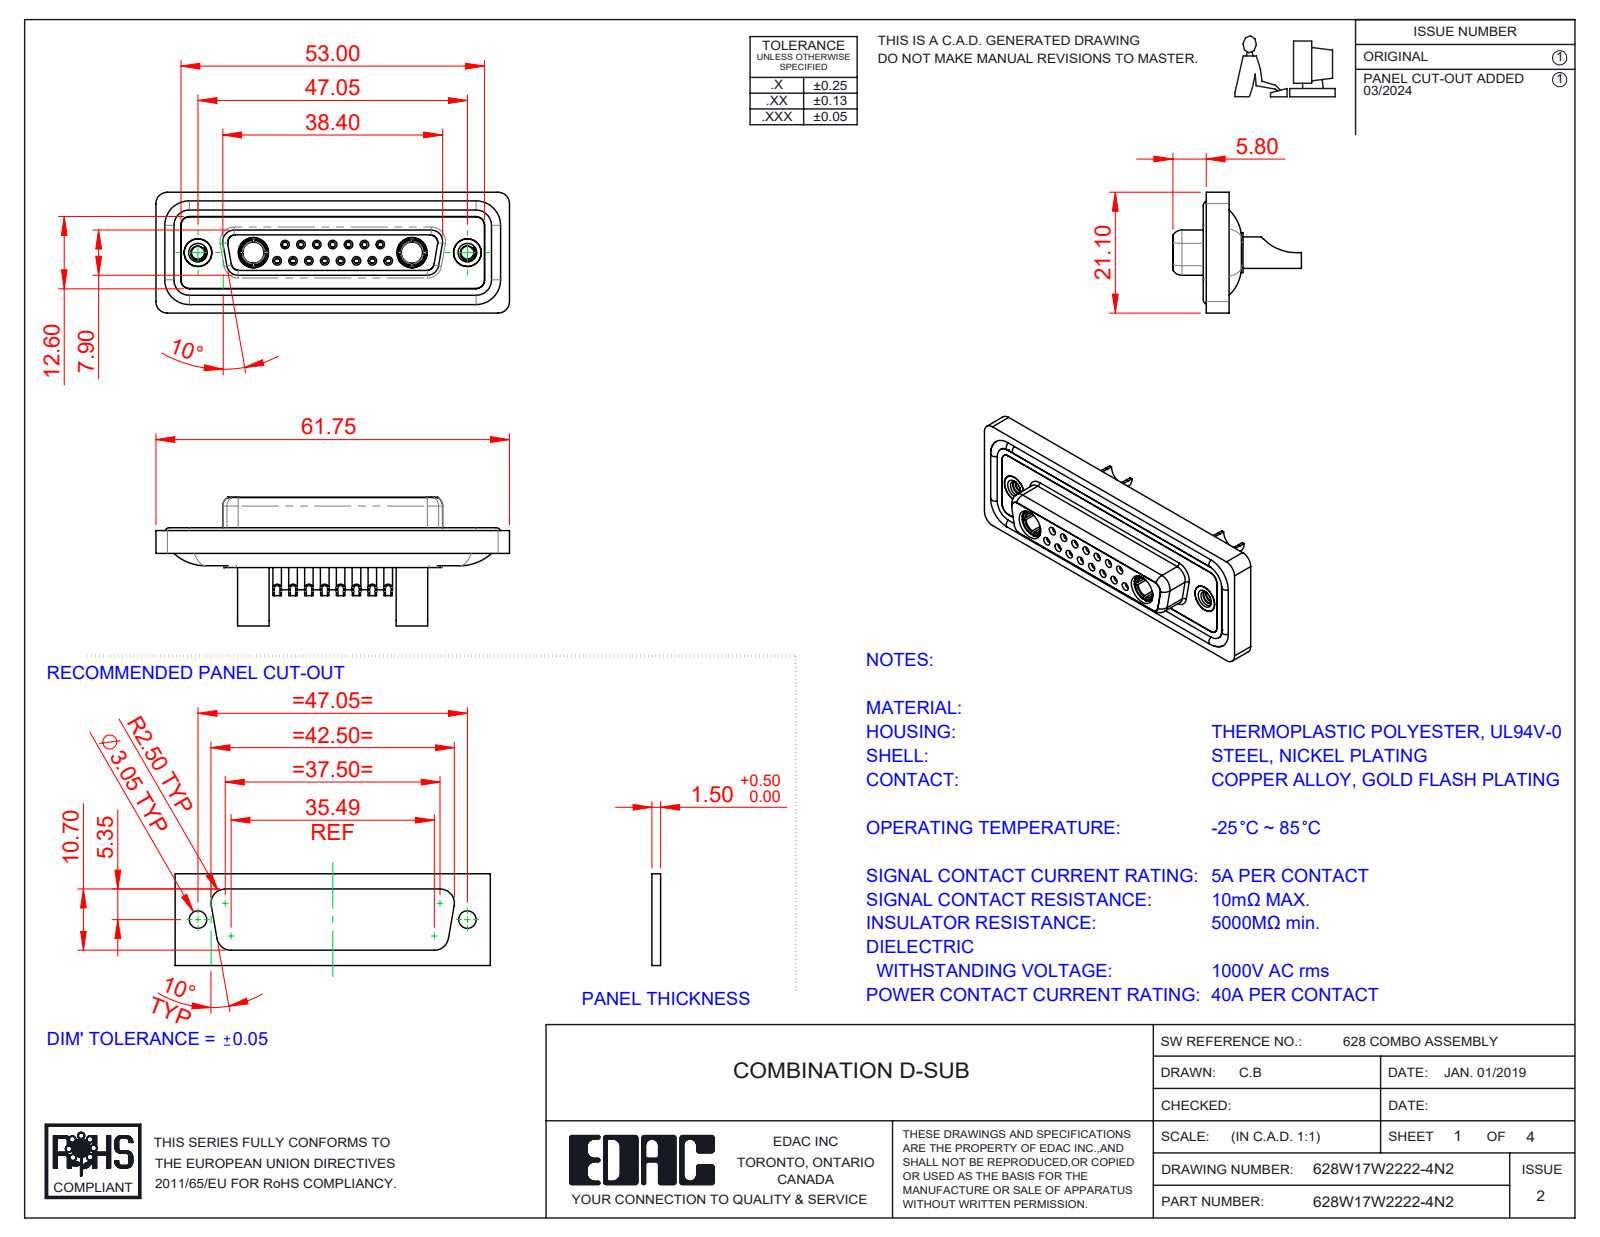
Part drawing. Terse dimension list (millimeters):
name: 628Combo Threaded Rivet_2; Power Socket_40A SC; 628Combo Contact Row 2_22; 628Combo Waterproof Housing_25 Contacts (+5 more)
written by: SolidWorks 2023 (CONFIG_CONTROL_DESIGN)
unit: mm
bodies: 26 solids, 1365 faces (422 planar, 551 cylindrical, 392 other)
size: 61.75 × 22.45 × 21.1
volume: 8 435 mm³; area: 14 295 mm²
holes: 15× ⌀0.9, 15× ⌀1, 15× ⌀1.1, 15× ⌀1.5, 15× ⌀2, 8× ⌀1.6, 7× ⌀1.7, 4× ⌀4.85, 2× ⌀2.26, 2× ⌀3.7, 2× ⌀4, 2× ⌀4.05
bosses: 15× ⌀2.2, 11× ⌀1.6, 2× ⌀5.5, 2× ⌀5.2, 2× ⌀4.96, 2× ⌀4.95, 2× ⌀4.8, 2× ⌀4.75
rounds: 22× R1.5, 18× R2, 8× R1.35, 8× R1.6, 6× R1, 4× R0.25, 4× R0.5, 4× R0.6
face distances: 0.4, 7.45, 1.8, 5.65, 6.6, 0.5, 7.05, 1.6, 2.9, 1.1
hole spacings: 3.16, 2.77, 8.31, 5.54, 5.03, 5.04, 7.49, 11.08
